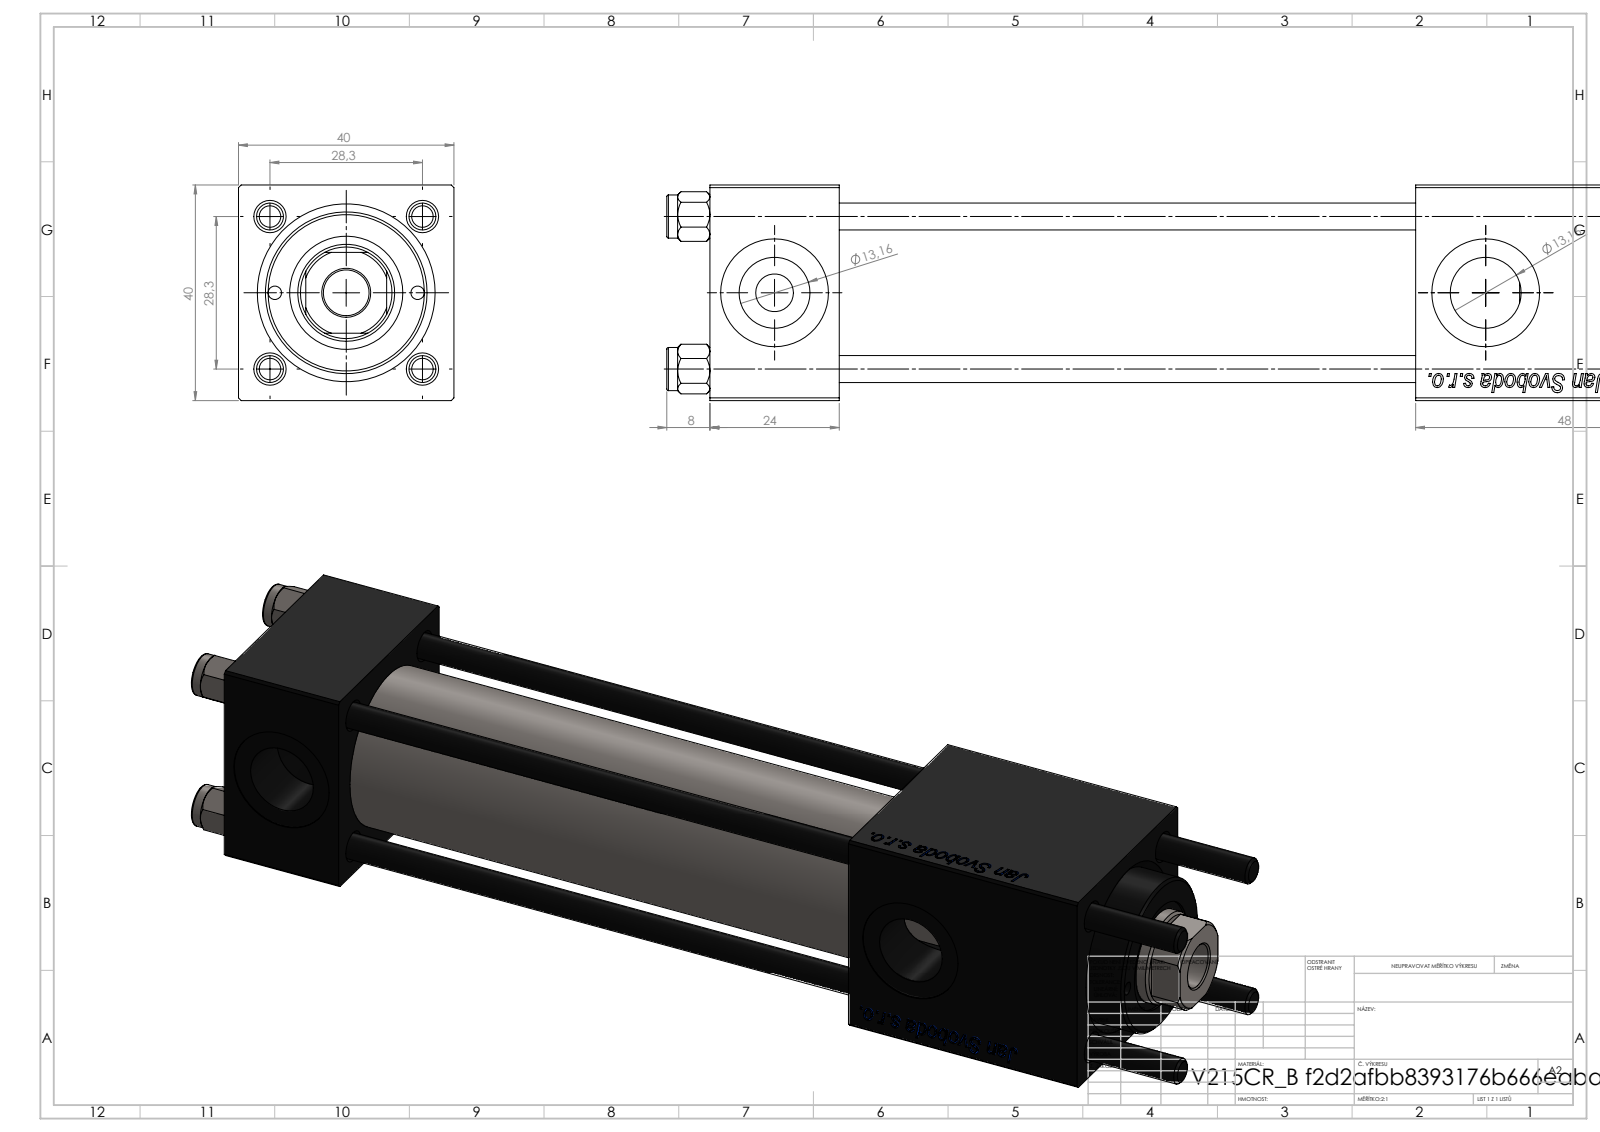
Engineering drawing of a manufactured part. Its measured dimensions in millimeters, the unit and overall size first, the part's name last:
Units: millimetres
Overall size (bounding box): 206 × 40 × 40
Round holes (diameter × count): ⌀5 ×4, ⌀20 ×3, ⌀2.5 ×2, ⌀7 ×2, ⌀13.16 ×2, ⌀8.5 ×1, ⌀18 ×1, ⌀21 ×1, ⌀25 ×1, ⌀30 ×1
Round bosses / shafts (diameter × count): ⌀8 ×4, ⌀31 ×1
Partial cylindrical surfaces — rounded edges, fillets, slot ends (radius × count): R8.5 ×1
Main face-to-face distances: 40, 24, 131, 107, 150.3, 126.3, 19.3, 179, 155, 48
Hole centre spacings: 14.18, 20.01, 28.3, 30.84, 13.25, 40.02, 26.5, 132
Volume: 188 188 mm³ · Surface area: 78 802 mm²
Bodies: 11 solids, 1158 faces (430 planar, 80 cylindrical, 648 other)
Part name (STEP PRODUCT): V215CR_VCP_B; V215CR_B_TYCINKA; NUT_M5_B; V215CR_B-1 (+1 more)
STEP written by: SolidWorks 2019 (CONFIG_CONTROL_DESIGN)
